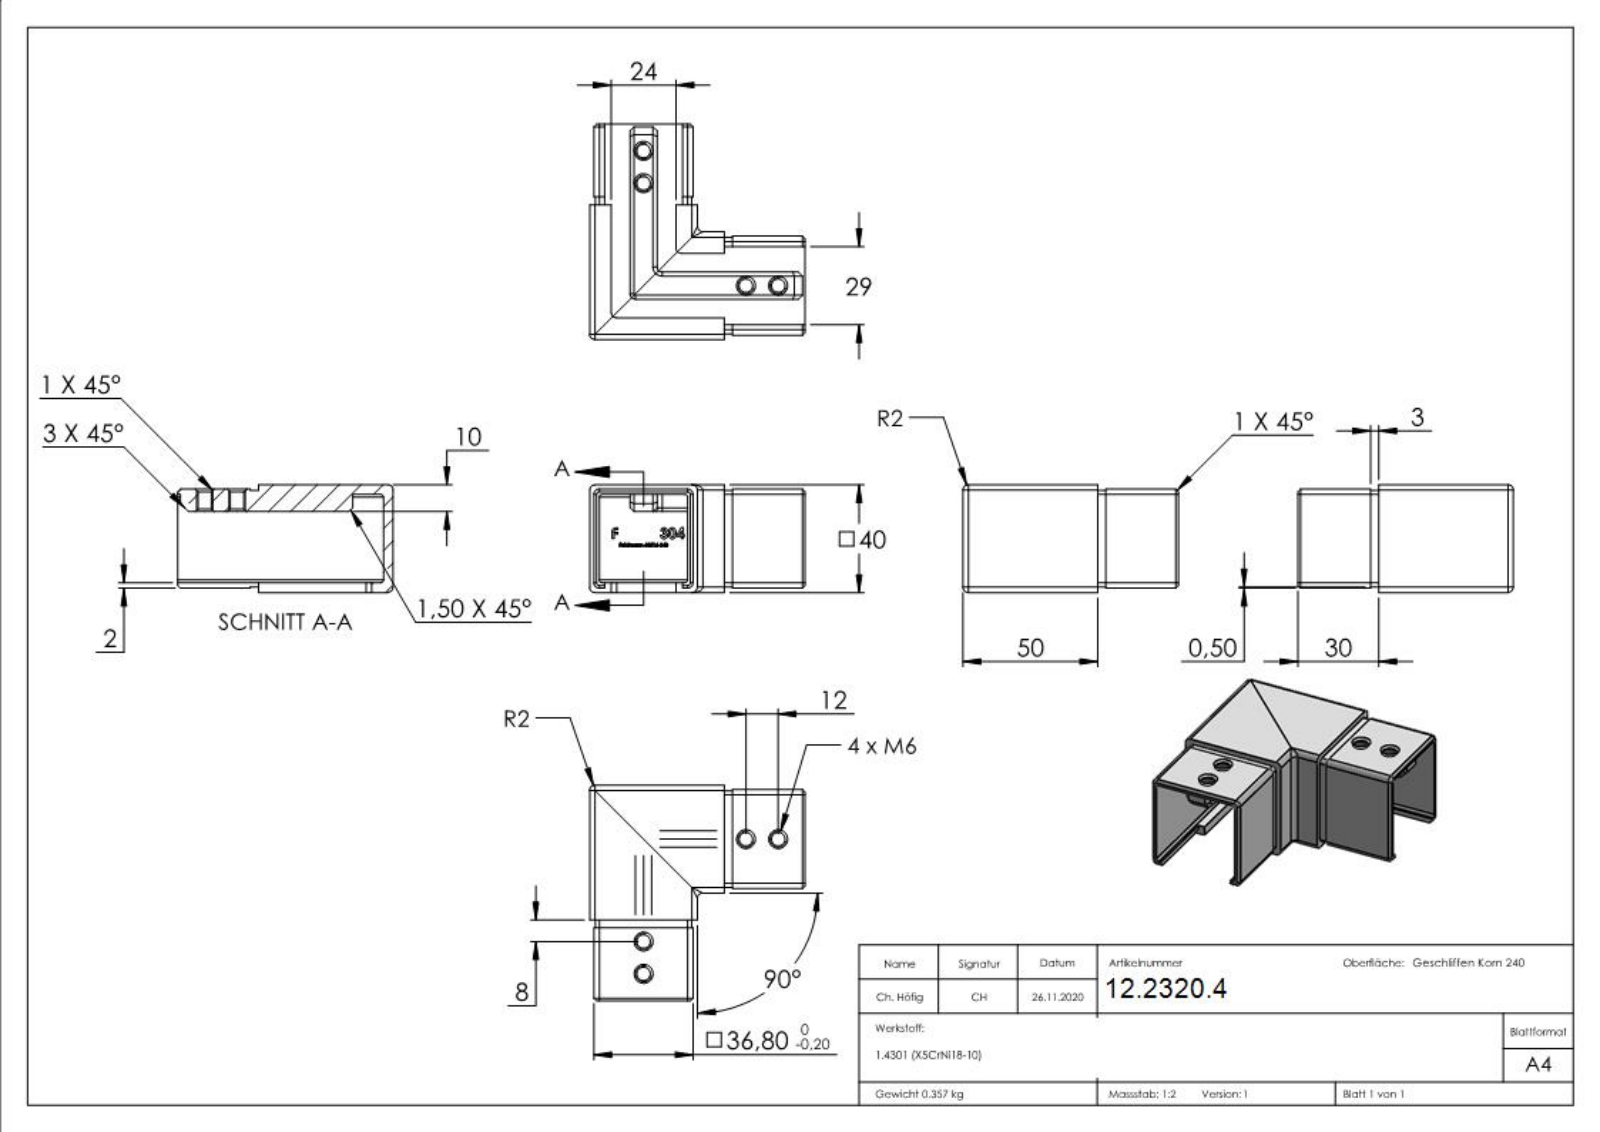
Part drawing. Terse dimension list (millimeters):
name: 60316-240
written by: SolidWorks 2018 (CONFIG_CONTROL_DESIGN)
unit: mm
bodies: 1 solid, 463 faces (256 planar, 46 cylindrical, 161 other)
size: 80 × 80 × 40
volume: 45 176 mm³; area: 30 408 mm²
holes: 4× ⌀5
rounds: 22× R2, 8× R1, 8× R1.5
face distances: 3.6, 2, 36.4, 34.8, 1.6, 32.8, 38.4, 36.8, 10, 25
hole spacings: 12, 62.8, 53.74, 70.71
